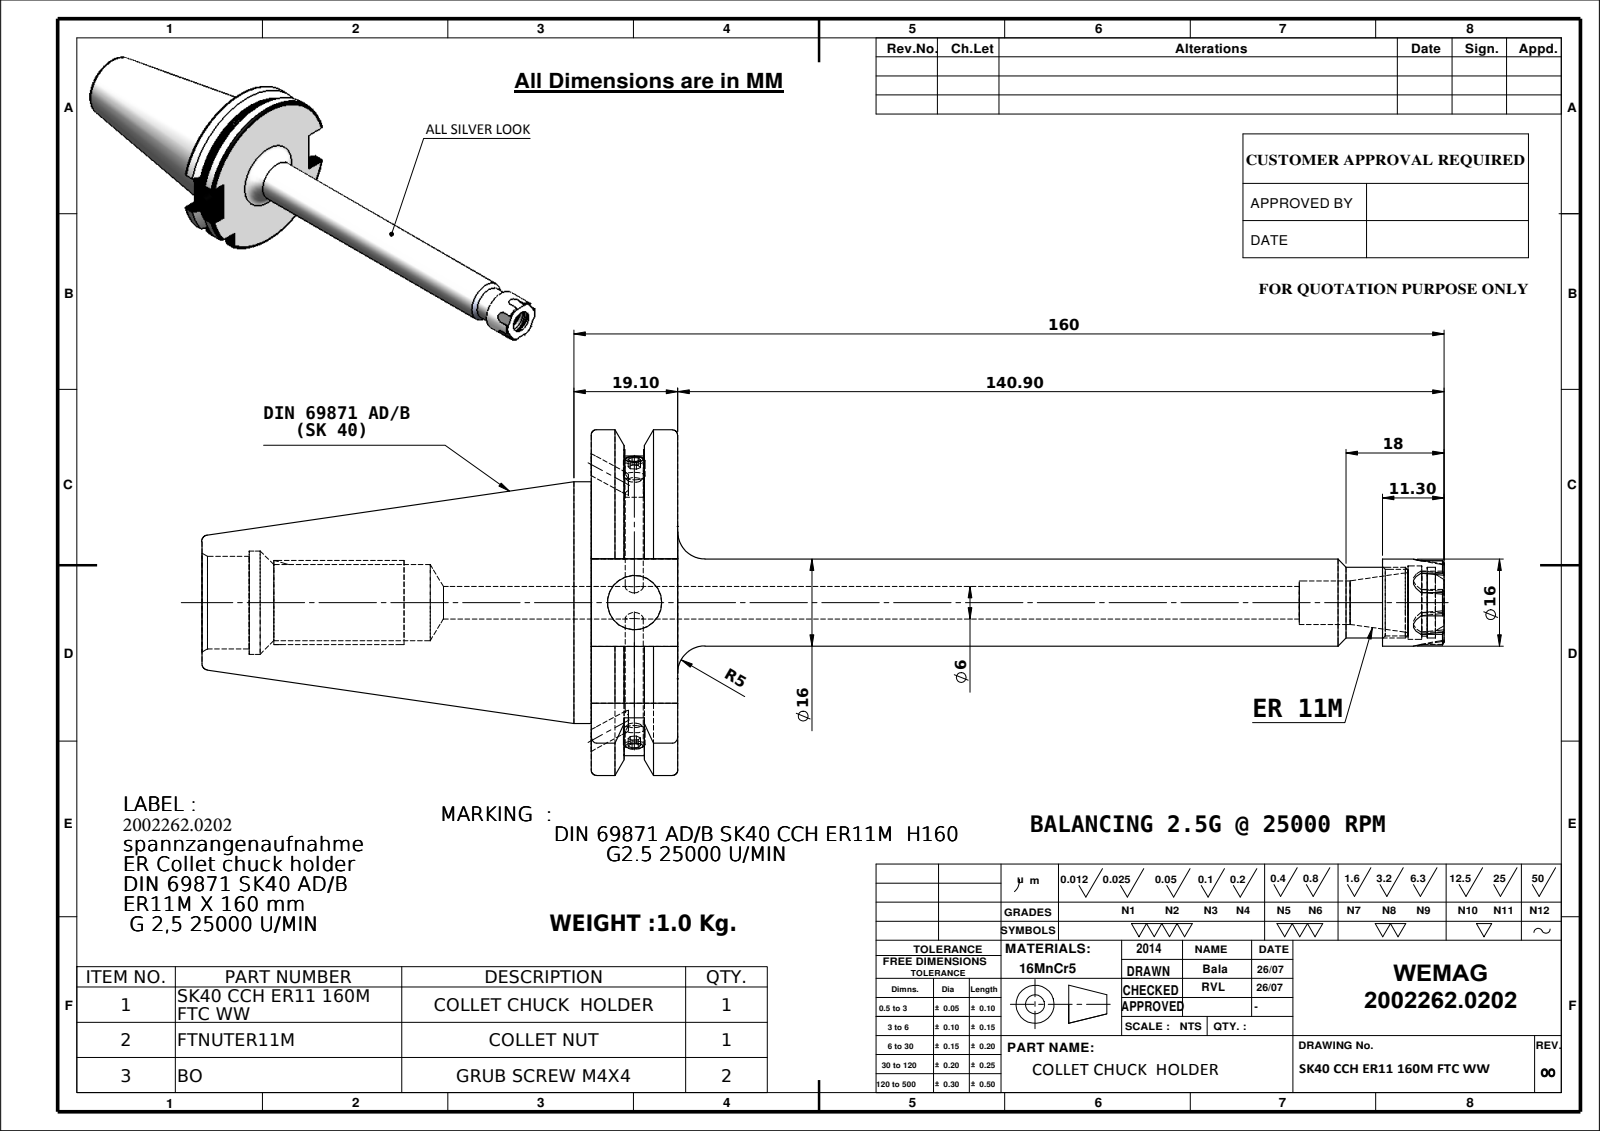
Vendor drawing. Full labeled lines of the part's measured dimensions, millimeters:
Part name (STEP PRODUCT): SK40 CCH ER11 160M FTC WW; M4X4_DIN 913 - M4 x 4-N; FTSCW71620; FTNUTER11M
STEP written by: SolidWorks 2009 (CONFIG_CONTROL_DESIGN)
Units: millimetres
Bodies: 5 solids, 205 faces (86 planar, 52 cylindrical, 67 other)
Overall size (bounding box): 228.4 × 63.55 × 61.48
Volume: 128 203 mm³ · Surface area: 32 129 mm²
Round holes (diameter × count): ⌀3.3 ×1, ⌀4 ×1, ⌀6 ×1, ⌀8 ×1, ⌀10 ×1, ⌀11.5 ×1, ⌀12.25 ×1, ⌀13 ×1, ⌀13.5 ×1, ⌀14 ×1, ⌀17 ×1, ⌀19 ×1
Round bosses / shafts (diameter × count): ⌀4 ×2, ⌀44.45 ×1, ⌀16 ×1, ⌀11.1 ×1
Partial cylindrical surfaces — rounded edges, fillets, slot ends (radius × count): R28.12 ×1, R31.77 ×1
Main face-to-face distances: 15.9, 16.1, 47.8, 87.5, 71.6, 140.9, 156.8, 228.4, 150.77, 9.87
Hole centre spacings: 0.75
